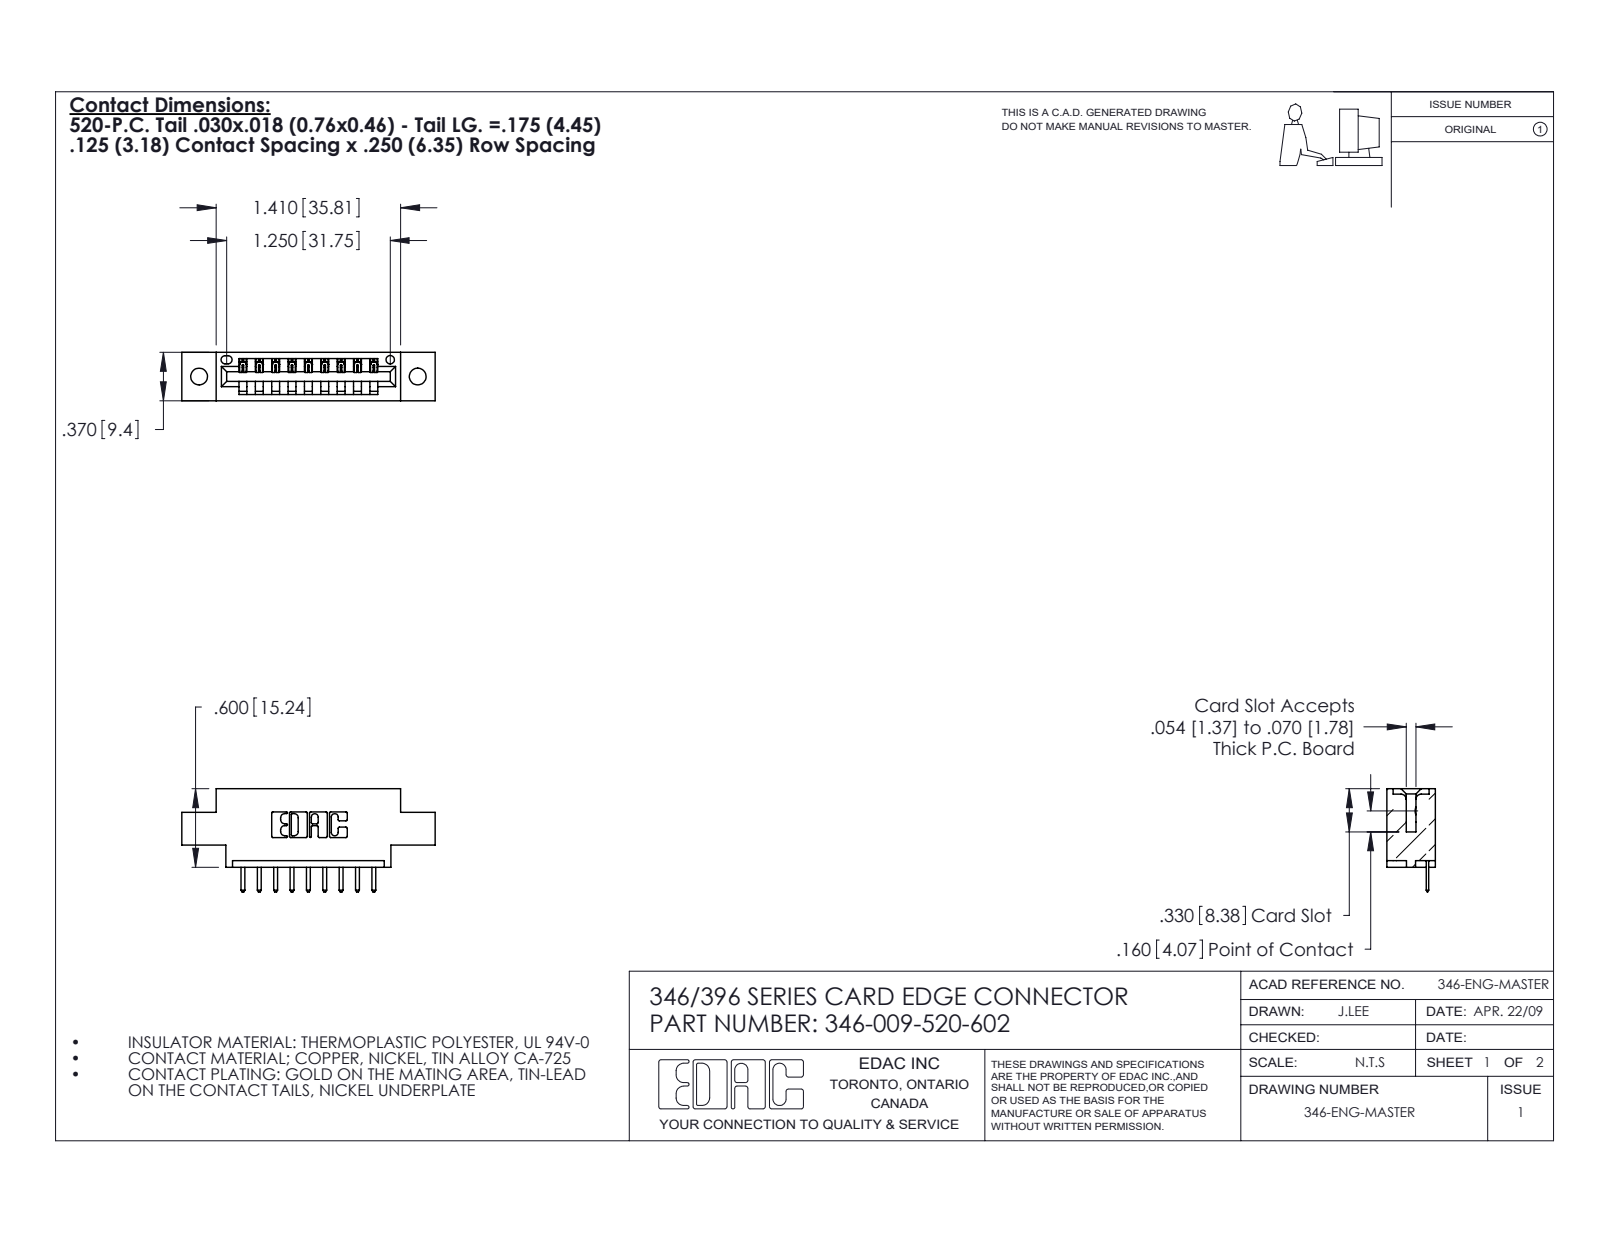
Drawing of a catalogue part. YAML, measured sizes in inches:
part_name: "346-009-520-602; 346 Part_0.170 Offset - 0.128 Dia; 345-292-001_345-293-120"
step_written_by: "SolidWorks 2020 (CONFIG_CONTROL_DESIGN)"
units: inches
bodies: {solids: 10, faces: 684, planar: 458, cylindrical: 226, other: 0}
overall_size: [1.935, 0.788, 0.37]
volume: 0.26
surface_area: 7.395
round_holes:
  - {diameter: 0.128, count: 2}
  - {diameter: 0.064, count: 1}
partial_cylinders:
  - {radius: 0.01, count: 22}
  - {radius: 0.01, count: 20}
  - {radius: 0.006, count: 18}
  - {radius: 0.007, count: 6}
  - {radius: 0.031, count: 6}
  - {radius: 0.026, count: 3}
  - {radius: 0.031, count: 2}
  - {radius: 0.04, count: 2}
face_to_face_distances: [0.25, 0.37, 0.048, 0.322, 0.148, 0.222, 0.1, 0.174, 0.072, 0.298]
hole_center_spacings: [0.246, 1.465, 1.67]
